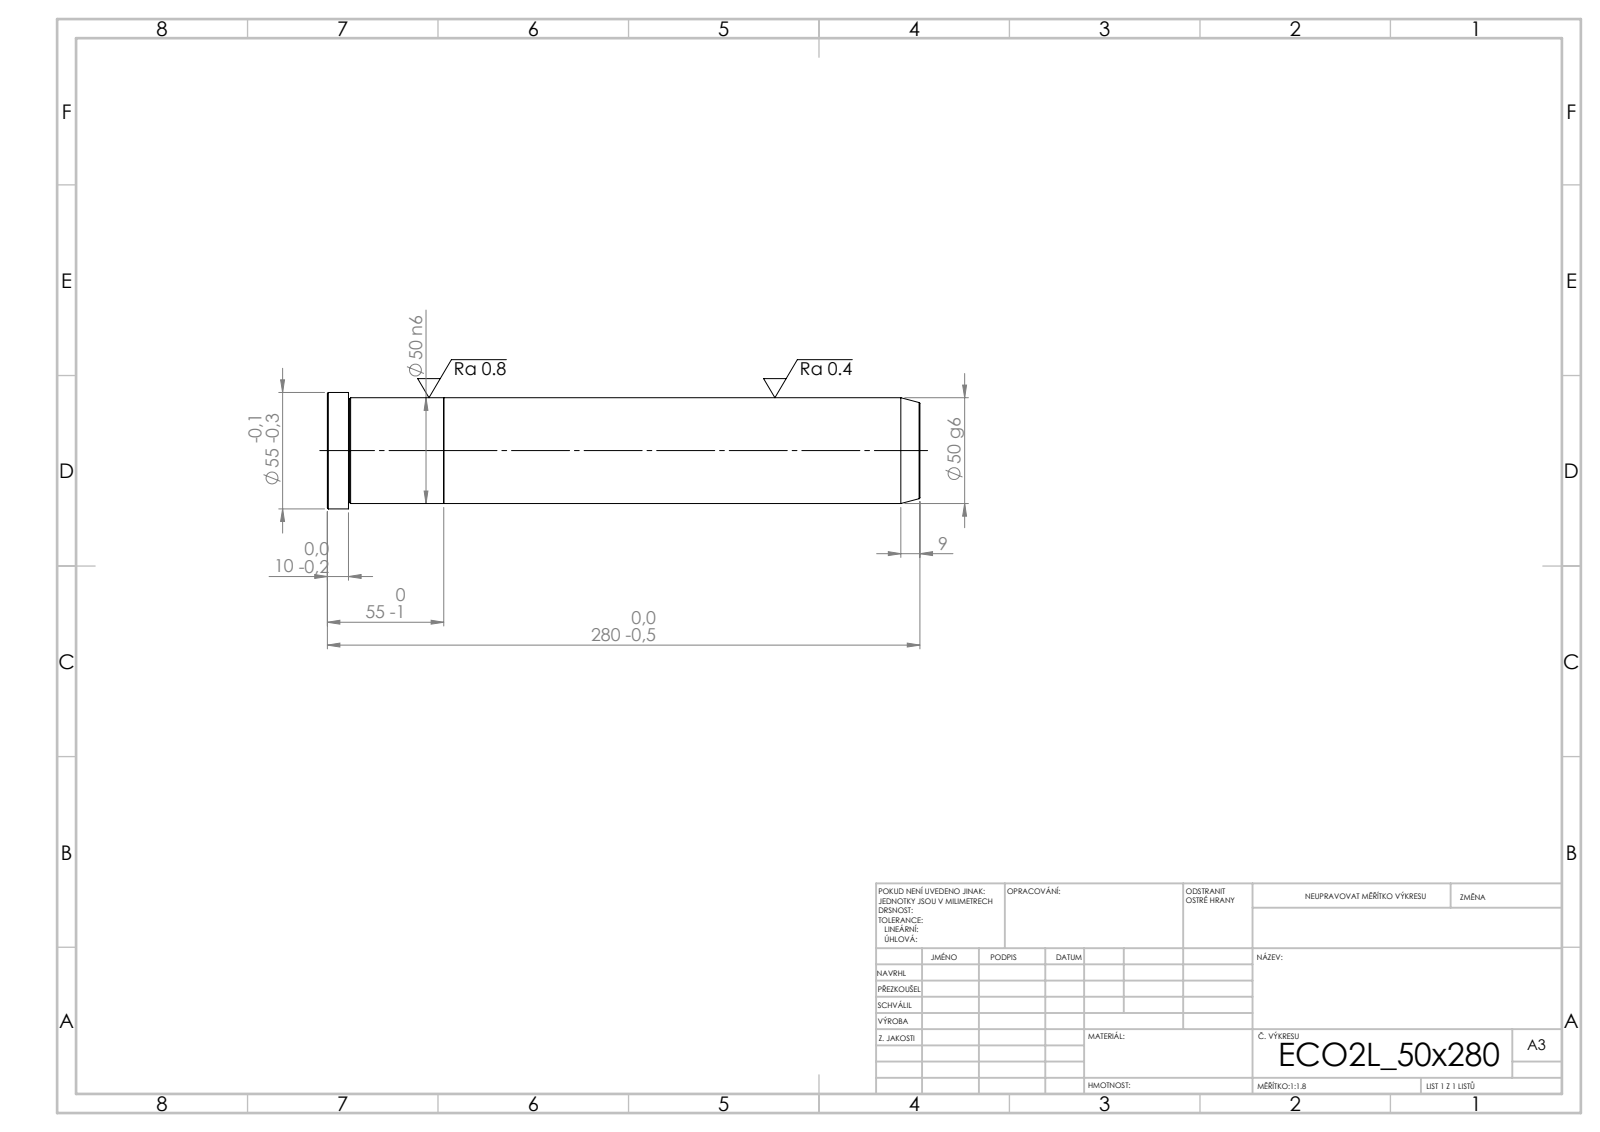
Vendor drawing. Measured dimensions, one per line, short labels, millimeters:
written by: SolidWorks 2019 (CONFIG_CONTROL_DESIGN)
unit: mm
bodies: 2 solids, 21 faces (5 planar, 6 cylindrical, 10 other)
size: 280 × 55 × 55
volume: 552 166 mm³; area: 52 456 mm²
bosses: 1× ⌀55, 1× ⌀50
face distances: 55, 225, 280, 270, 45, 10
